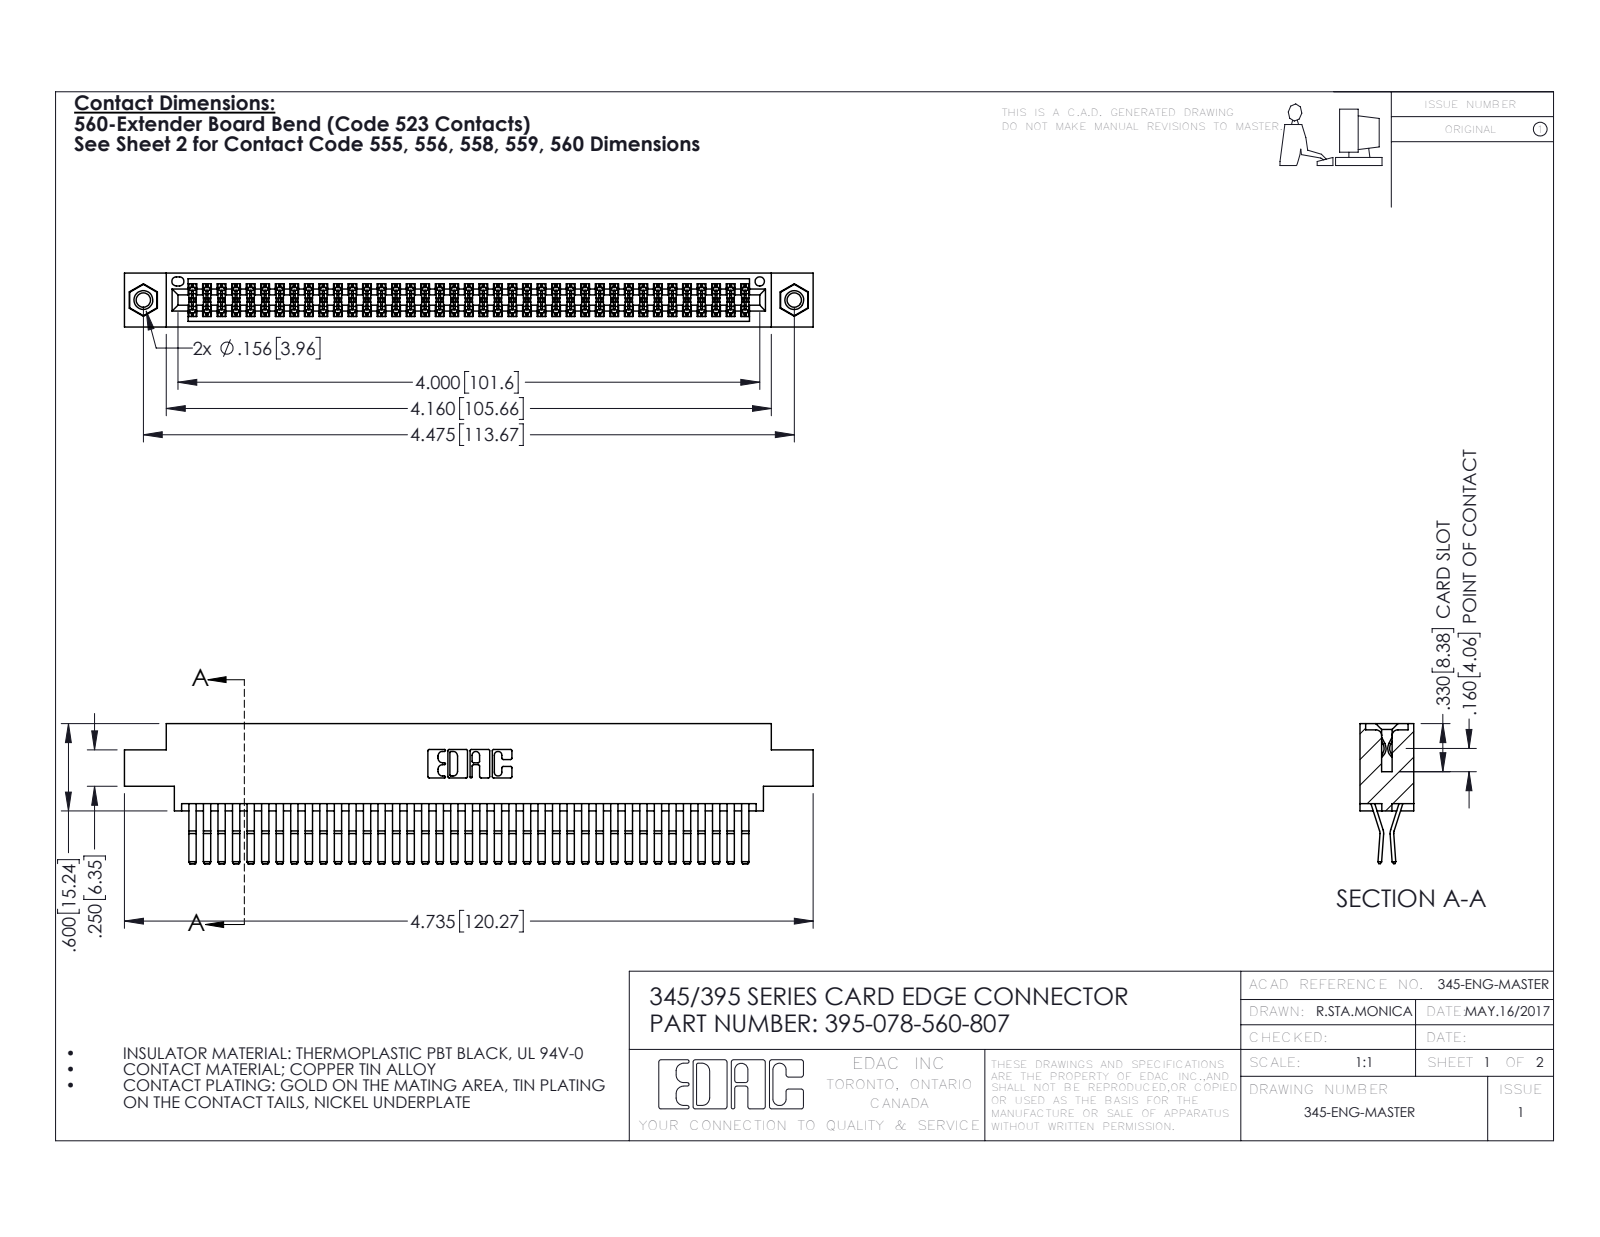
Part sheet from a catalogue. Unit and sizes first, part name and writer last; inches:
Units: inches
Overall size (bounding box): 4.735 × 0.962 × 0.37
Round holes (diameter × count): ⌀0.098 ×2, ⌀0.125 ×2, ⌀0.156 ×2, ⌀0.064 ×1
Round bosses / shafts (diameter × count): ⌀0.155 ×2
Partial cylindrical surfaces — rounded edges, fillets, slot ends (radius × count): R0.006 ×117, R0.01 ×22, R0.007 ×6, R0.031 ×6, R0.026 ×3, R0.01 ×2, R0.014 ×2, R0.019 ×2
Main face-to-face distances: 0.025, 0.072, 0.298, 0.37, 0.2, 0.098, 0.272, 0.225, 0.175, 0.149
Hole centre spacings: 0.27, 4.239, 4.475
Volume: 0.735 in³ · Surface area: 29.8 in²
Bodies: 81 solids, 4246 faces (2690 planar, 1540 cylindrical, 16 other)
Part name (STEP PRODUCT): 345 Part_0.170 Offset - 0.156 Dia-TI; 345-292-001_560 Tail; 395-078-560-807; 345-250-001_345-250-005-103
STEP written by: SolidWorks 2016 (CONFIG_CONTROL_DESIGN)
